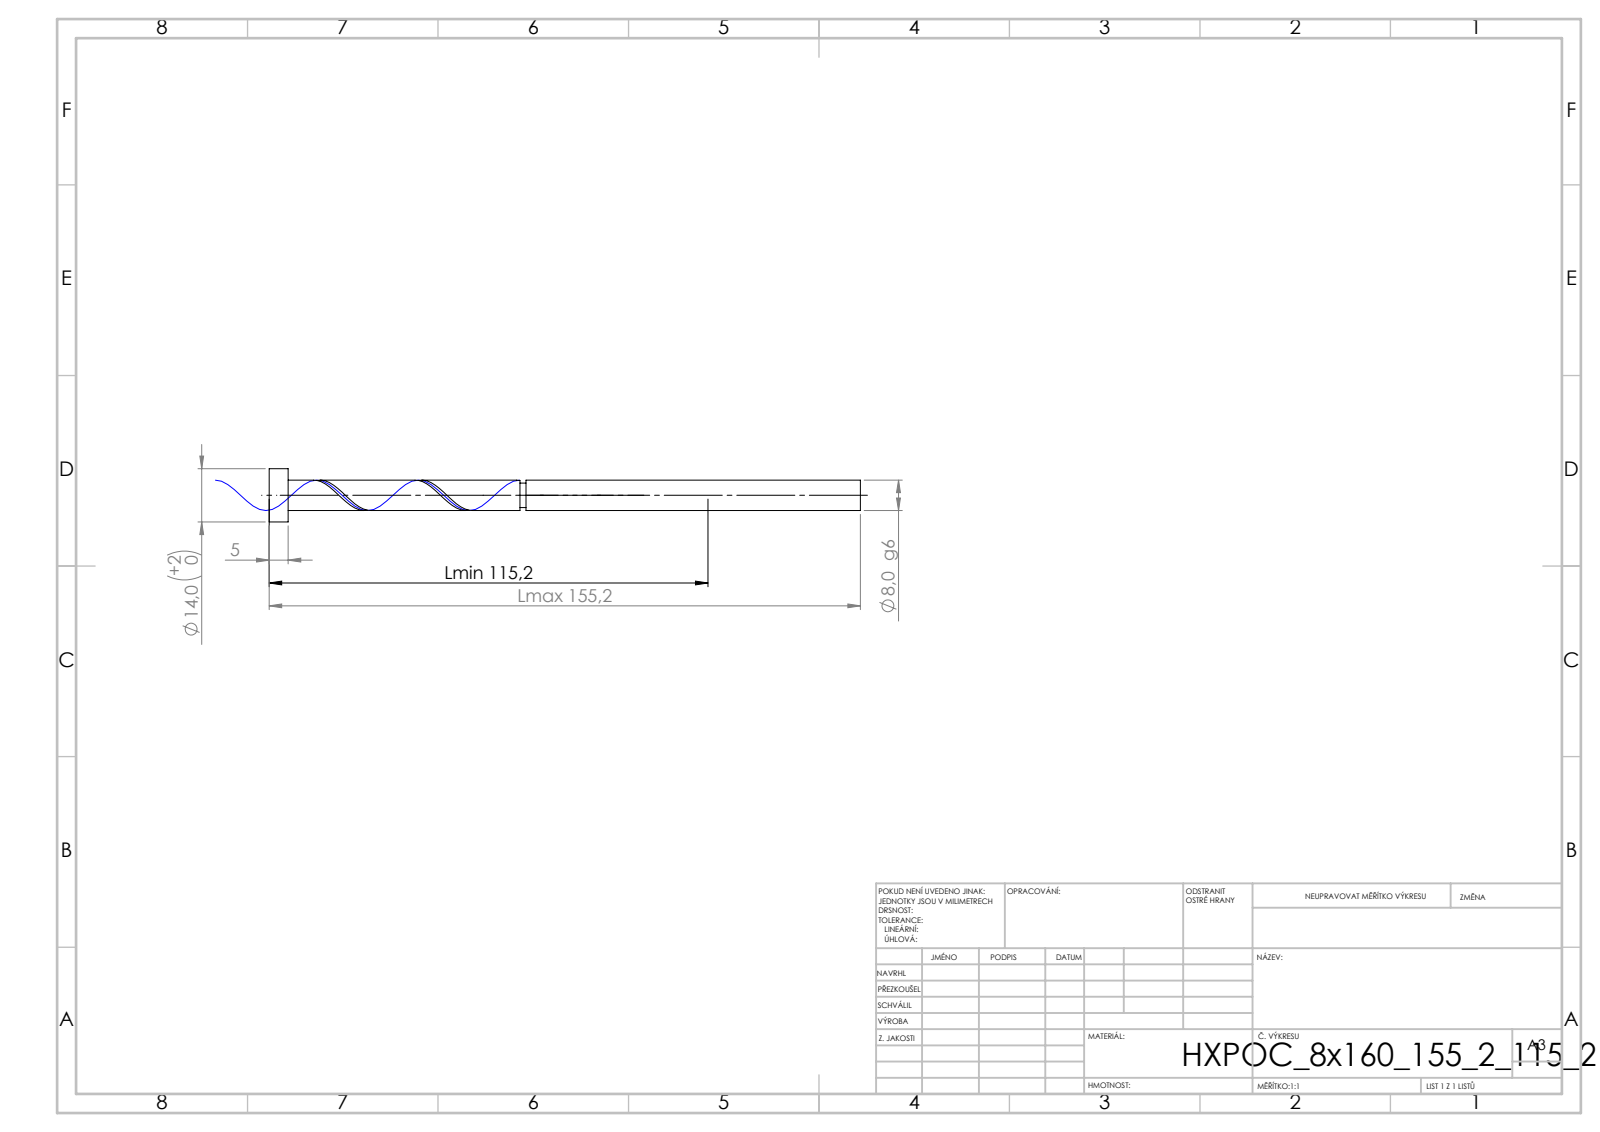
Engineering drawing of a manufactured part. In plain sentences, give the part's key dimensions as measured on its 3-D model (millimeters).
Its 3-D file was written by "SolidWorks 2019 (CONFIG_CONTROL_DESIGN)". It is 1 solid with 20 faces: 5 planar, 13 cylindrical and 2 other. Overall it measures 155.2 by 14 by 14 millimeters. Its volume is 8 227 cubic millimeters and its surface area 4 424 square millimeters. Round bosses or shafts: 1 of diameter 14, 1 of diameter 8, 1 of diameter 6.4. The main face-to-face distances are 5, 155.2, 150.2, 67.42, 62.42, 87.78, 65.82, 60.82, 1.6, 89.38.
